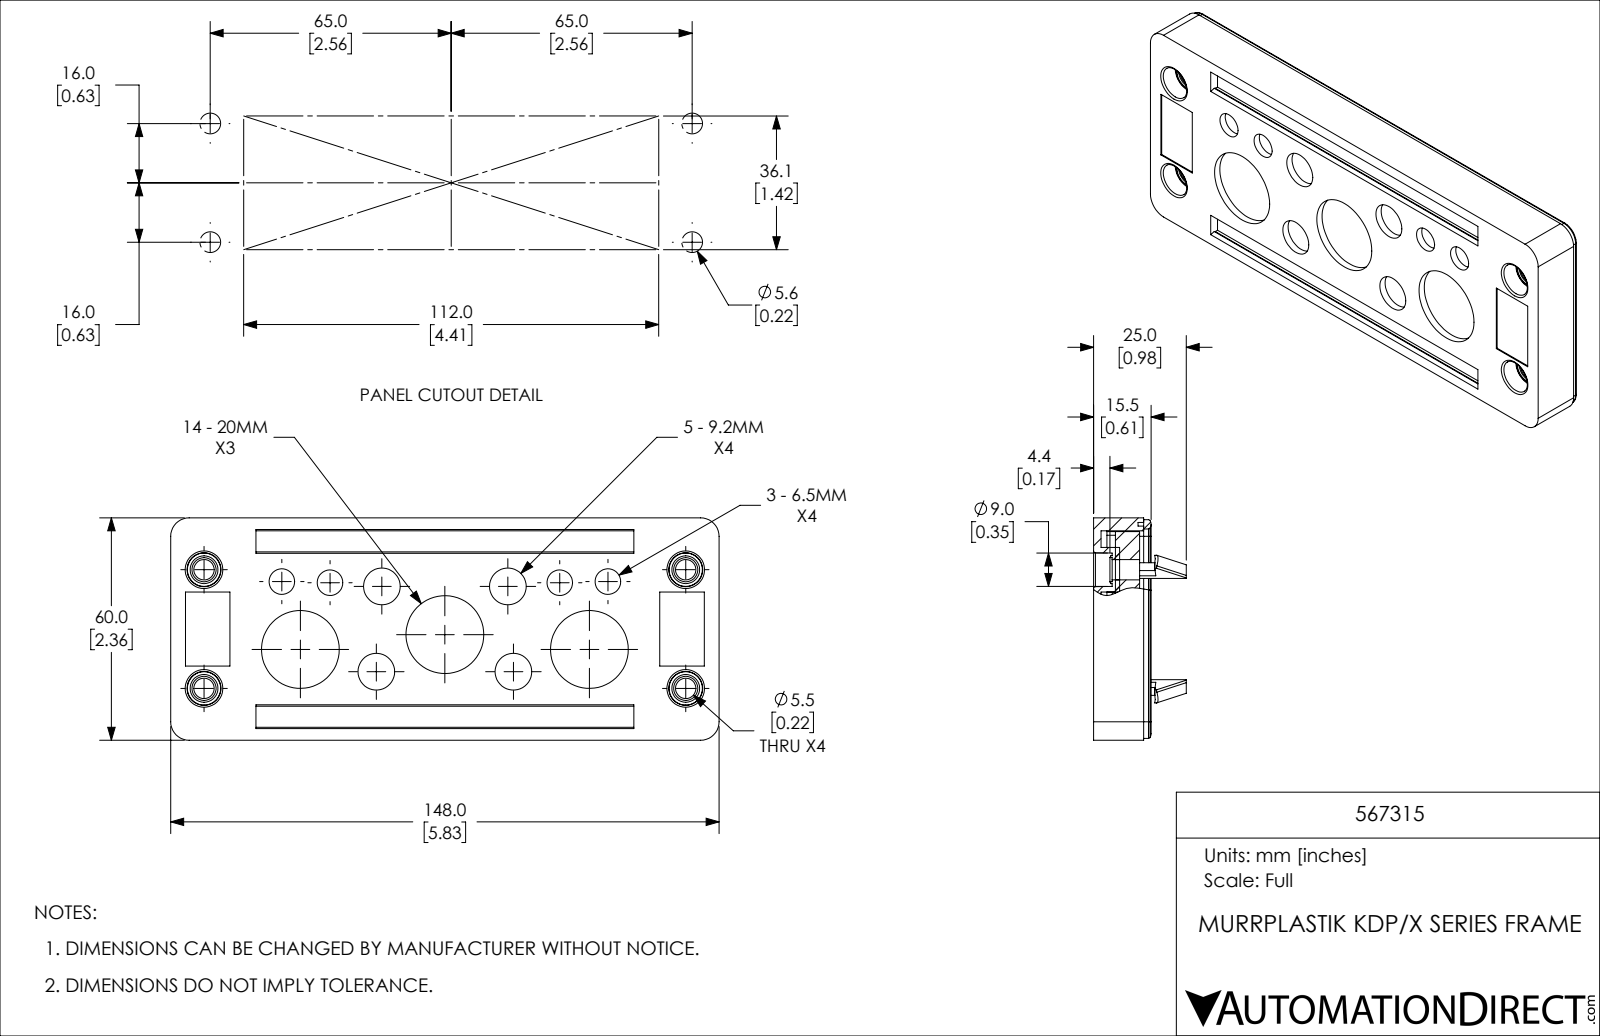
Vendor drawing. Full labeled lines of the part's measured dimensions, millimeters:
Part name (STEP PRODUCT): 567315
STEP written by: SolidWorks 2019 (CONFIG_CONTROL_DESIGN)
Units: millimetres
Bodies: 4 solids, 382 faces (178 planar, 168 cylindrical, 36 other)
Overall size (bounding box): 148 × 60 × 25
Volume: 79 479 mm³ · Surface area: 63 408 mm²
Round holes (diameter × count): ⌀5.5 ×4, ⌀6.5 ×4, ⌀6.9 ×4, ⌀9.9 ×4, ⌀11 ×4, ⌀13.8 ×4, ⌀21 ×3, ⌀25 ×3
Round bosses / shafts (diameter × count): ⌀7.5 ×4
Partial cylindrical surfaces — rounded edges, fillets, slot ends (radius × count): R2 ×12, R0.5 ×8, R1 ×8, R3 ×8, R1.5 ×4, R2.75 ×4, R3.25 ×4, R3.5 ×4
Main face-to-face distances: 2.3, 5.9, 3.6, 6.5, 12.4, 8.8, 2, 1.6, 3.9, 10.4
Hole centre spacings: 13, 14.04, 18.97, 19.7, 21.03, 21.24, 21.36, 21.4
